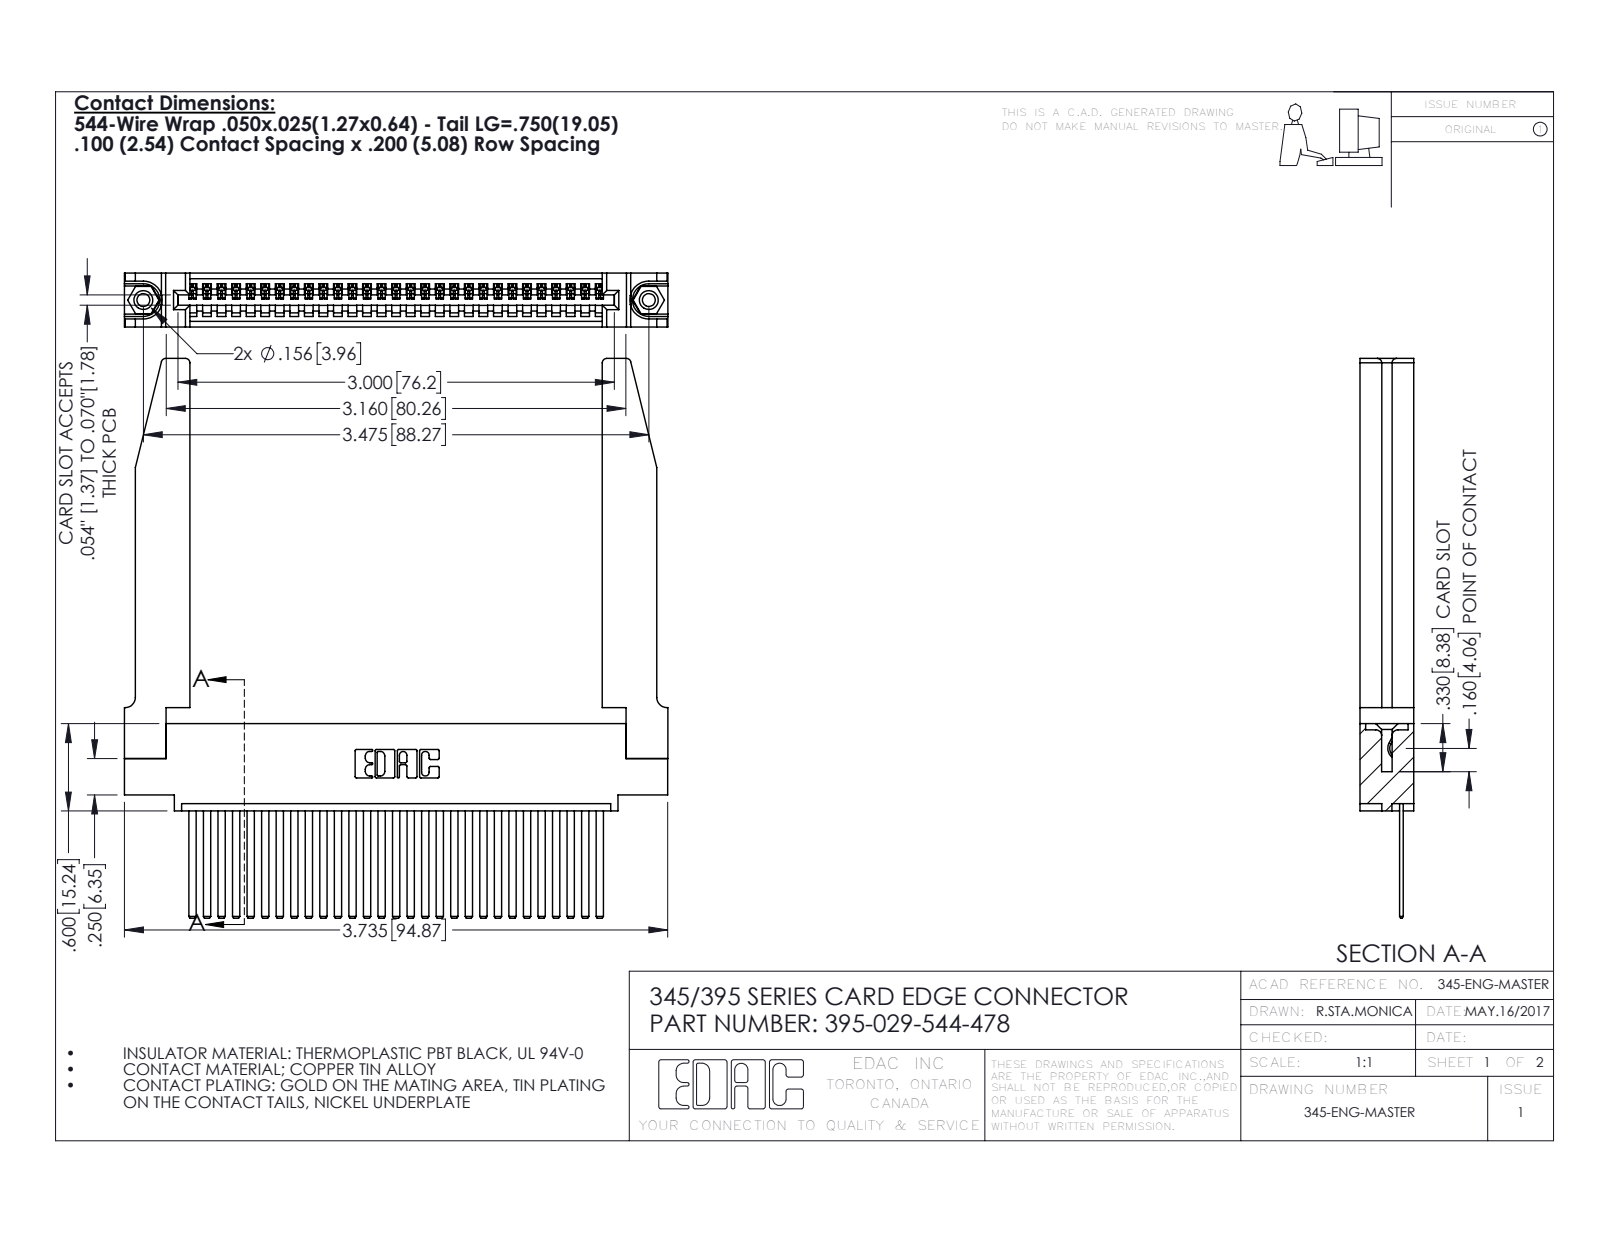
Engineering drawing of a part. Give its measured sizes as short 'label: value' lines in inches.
name: 345 Part_0.110 Offset - 0.156 Dia-TH; 345-250-001_345-250-001-102; 345-292-001_345-293-144; 395-029-544-478 (+1 more)
written by: SolidWorks 2016 (CONFIG_CONTROL_DESIGN)
unit: in
bodies: 34 solids, 1872 faces (1270 planar, 550 cylindrical, 52 other)
size: 3.847 × 3.736 × 0.37
volume: 1.034 in³; area: 30.91 in²
holes: 2× ⌀0.089, 2× ⌀0.125, 2× ⌀0.156, 1× ⌀0.064
bosses: 2× ⌀0.155
rounds: 58× R0.006, 22× R0.01, 8× R0.03, 6× R0.007, 6× R0.031, 3× R0.026, 2× R0.031, 2× R0.04
face distances: 0.072, 0.37, 0.298, 0.098, 0.272, 0.025, 0.2, 0.148, 0.15, 0.225
hole spacings: 0.27, 3.24, 3.475
